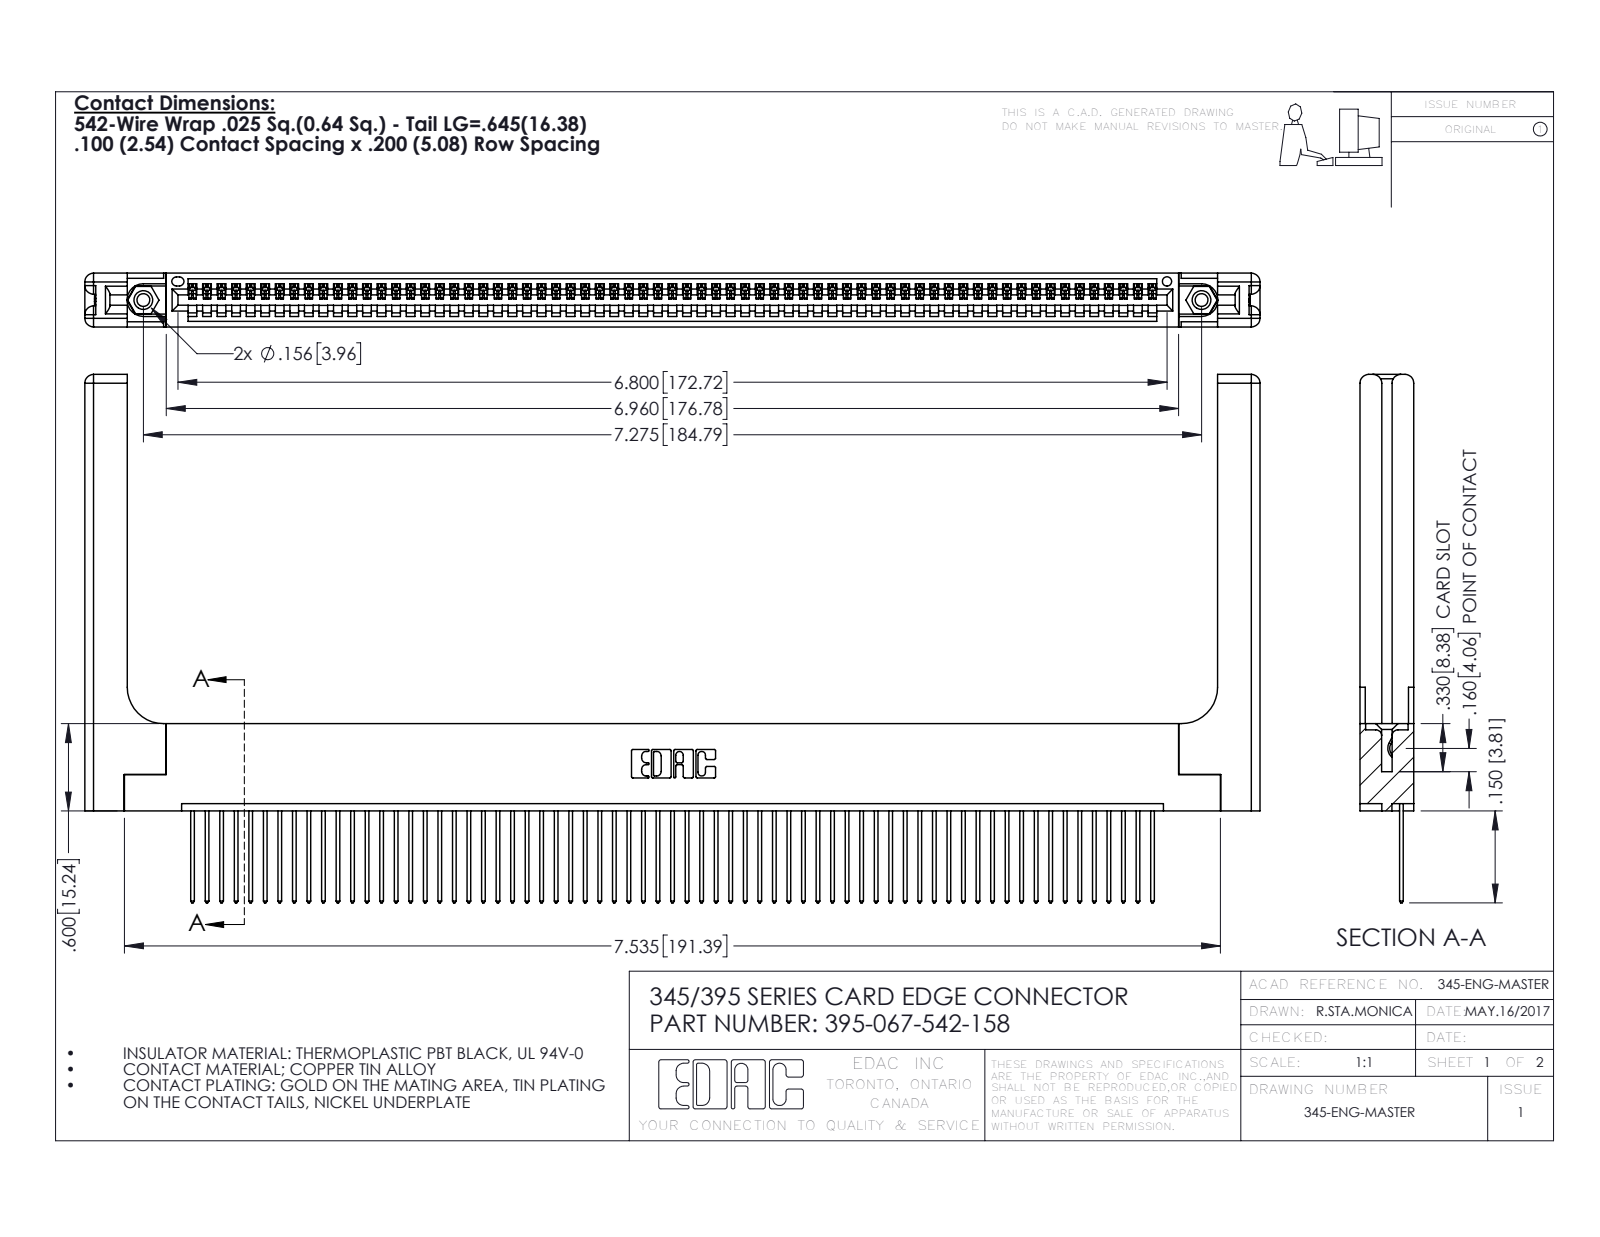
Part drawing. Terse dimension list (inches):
name: 345-220-058_345-220-058; 345-250-001_345-250-001-102; 345 Part_Flush Mounting Lugs - 0.156 Dia-TH; 345-292-001_345-293-142 (+1 more)
written by: SolidWorks 2016 (CONFIG_CONTROL_DESIGN)
unit: in
bodies: 72 solids, 4268 faces (2908 planar, 1300 cylindrical, 60 other)
size: 8.079 × 3.632 × 0.37
volume: 1.73 in³; area: 51.09 in²
holes: 2× ⌀0.089, 2× ⌀0.125, 2× ⌀0.156, 1× ⌀0.064
bosses: 2× ⌀0.155
rounds: 134× R0.006, 134× R0.01, 22× R0.01, 16× R0.06, 6× R0.007, 6× R0.031, 3× R0.026, 2× R0.03
face distances: 0.072, 0.298, 0.37, 0.098, 0.272, 0.025, 0.2, 0.225, 0.148, 0.15
hole spacings: 0.27, 7.039, 7.275
